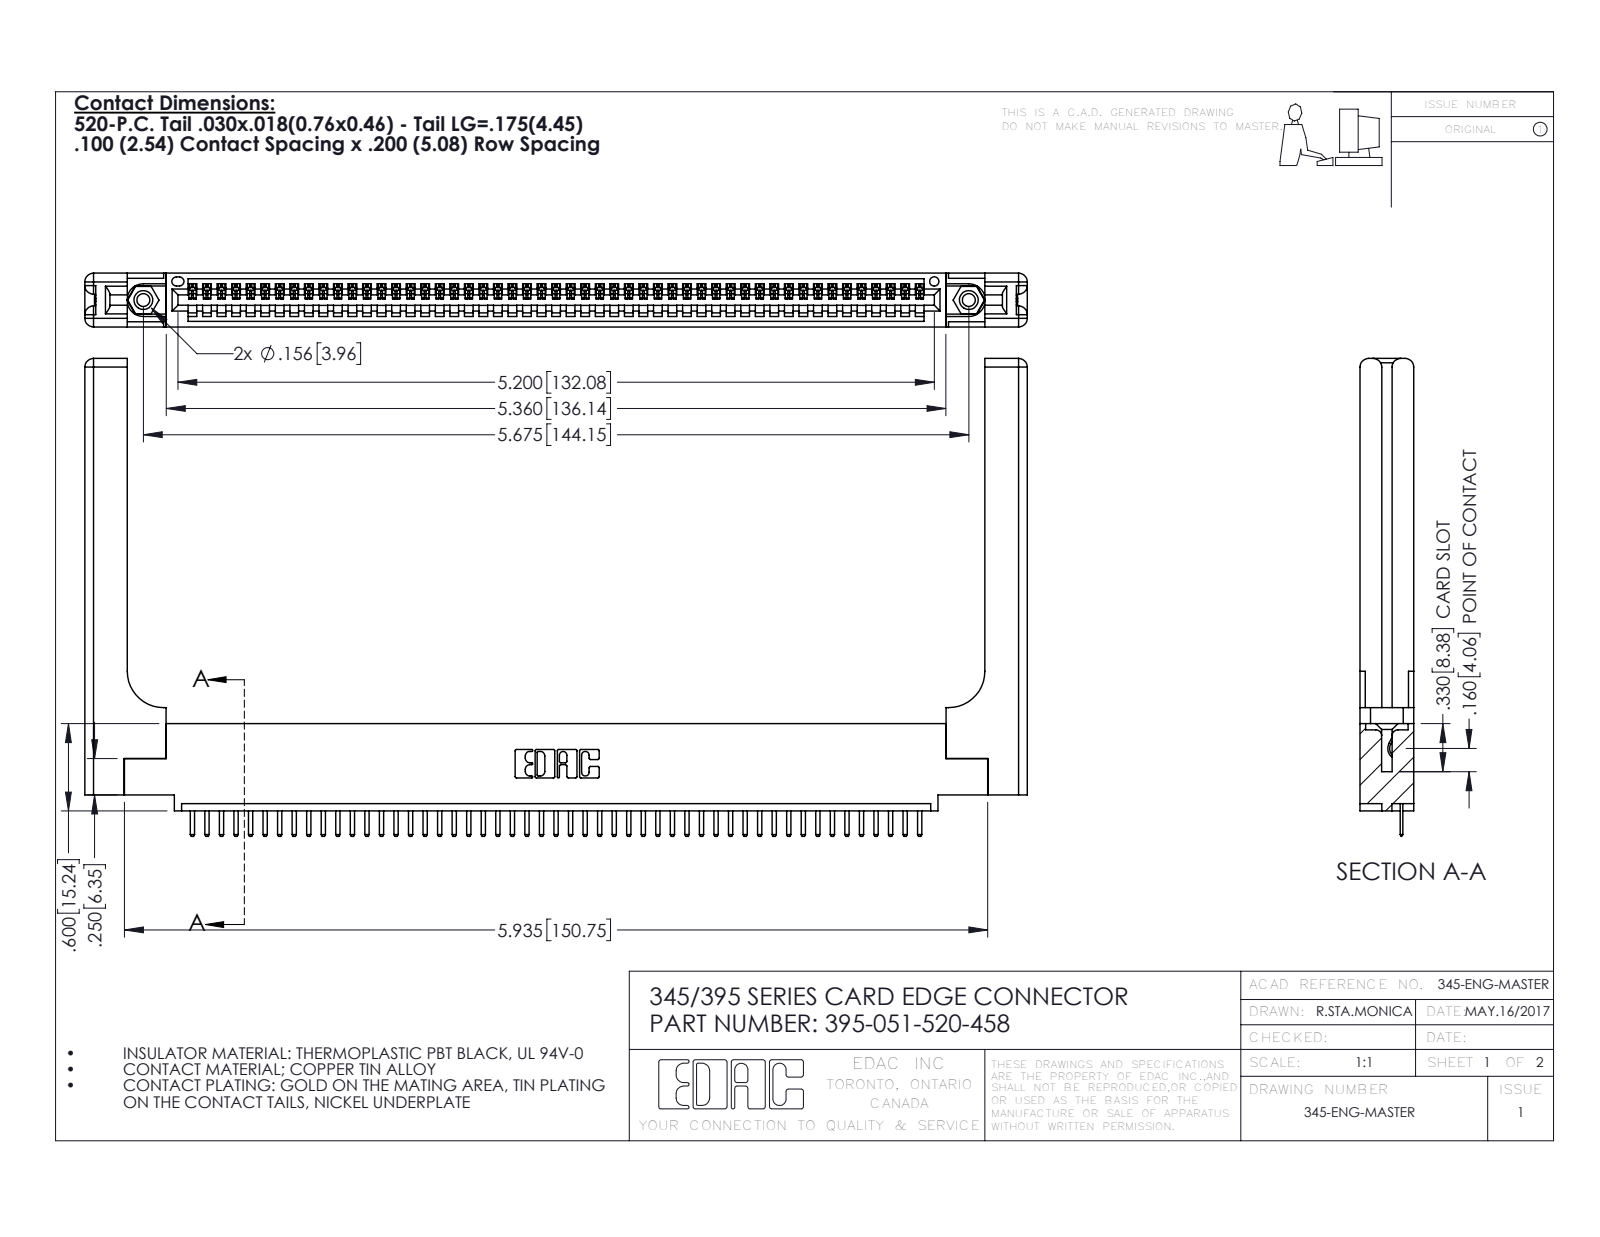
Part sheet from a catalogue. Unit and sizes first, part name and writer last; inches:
Units: inches
Overall size (bounding box): 6.479 × 3.285 × 0.37
Round holes (diameter × count): ⌀0.089 ×2, ⌀0.125 ×2, ⌀0.156 ×2, ⌀0.064 ×1
Round bosses / shafts (diameter × count): ⌀0.155 ×2
Partial cylindrical surfaces — rounded edges, fillets, slot ends (radius × count): R0.01 ×104, R0.006 ×102, R0.01 ×22, R0.06 ×16, R0.007 ×6, R0.031 ×6, R0.026 ×3, R0.03 ×2
Main face-to-face distances: 0.37, 0.072, 0.298, 0.098, 0.272, 0.025, 0.2, 0.225, 0.148, 0.15
Hole centre spacings: 0.27, 5.439, 5.675
Volume: 1.464 in³ · Surface area: 39.69 in²
Bodies: 56 solids, 3548 faces (2374 planar, 1114 cylindrical, 60 other)
Part name (STEP PRODUCT): 395-051-520-458; 345-250-001_345-250-001-102; 345-292-001_345-293-120; 345 Part_0.110 Offset - 0.156 Dia-TH (+1 more)
STEP written by: SolidWorks 2016 (CONFIG_CONTROL_DESIGN)
